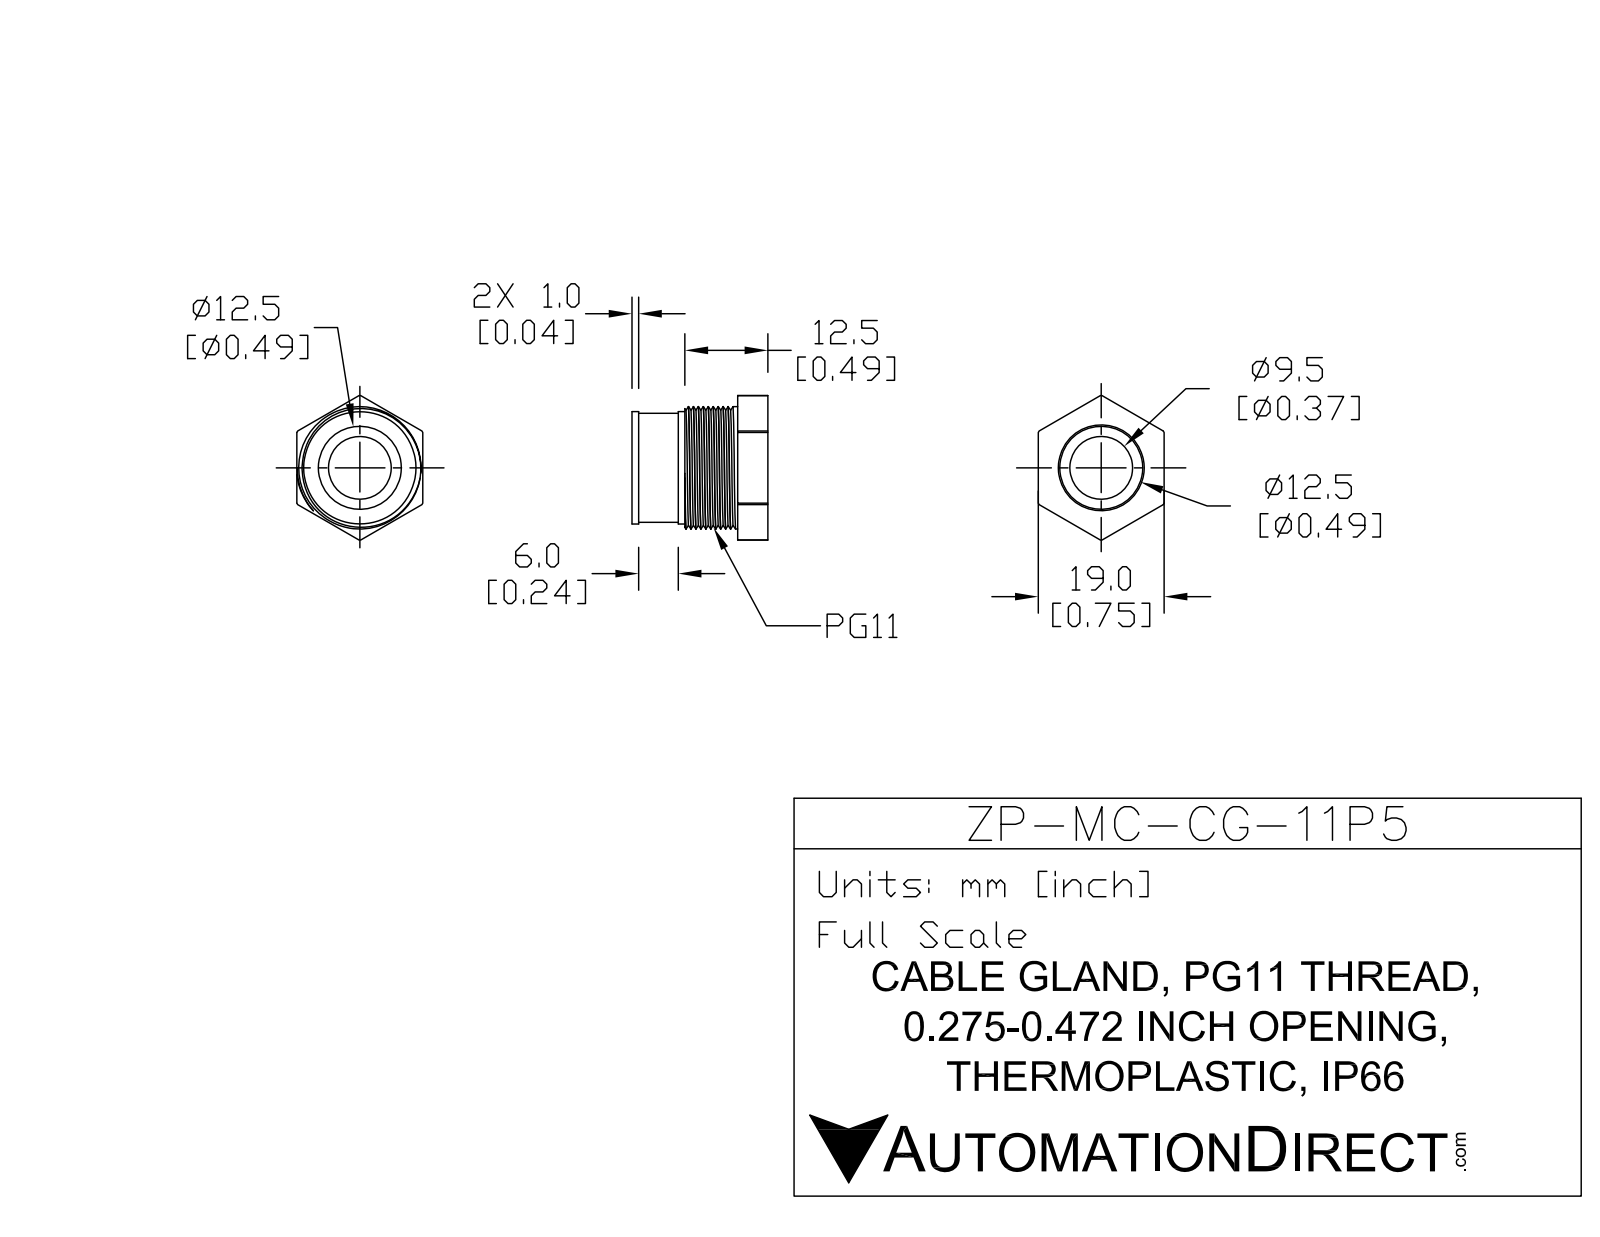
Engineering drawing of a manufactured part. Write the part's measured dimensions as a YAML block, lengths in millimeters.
part_name: "ZP-MC-CG-11P5"
step_written_by: "SolidWorks 2011 (AUTOMOTIVE_DESIGN)"
units: millimeters
bodies: {solids: 1, faces: 47, planar: 17, cylindrical: 25, other: 5}
overall_size: [21.85, 20.5, 19.05]
volume: 2978
surface_area: 2730
round_holes:
  - {diameter: 9.5, count: 1}
  - {diameter: 12.5, count: 1}
round_bosses_or_shafts:
  - {diameter: 18.5, count: 1}
  - {diameter: 17, count: 1}
  - {diameter: 16.5, count: 1}
partial_cylinders:
  - {radius: 9.59, count: 1}
  - {radius: 10.93, count: 1}
face_to_face_distances: [20.5, 1, 7, 19.04, 8, 13.5, 19.5, 6, 19.06, 4.5]
